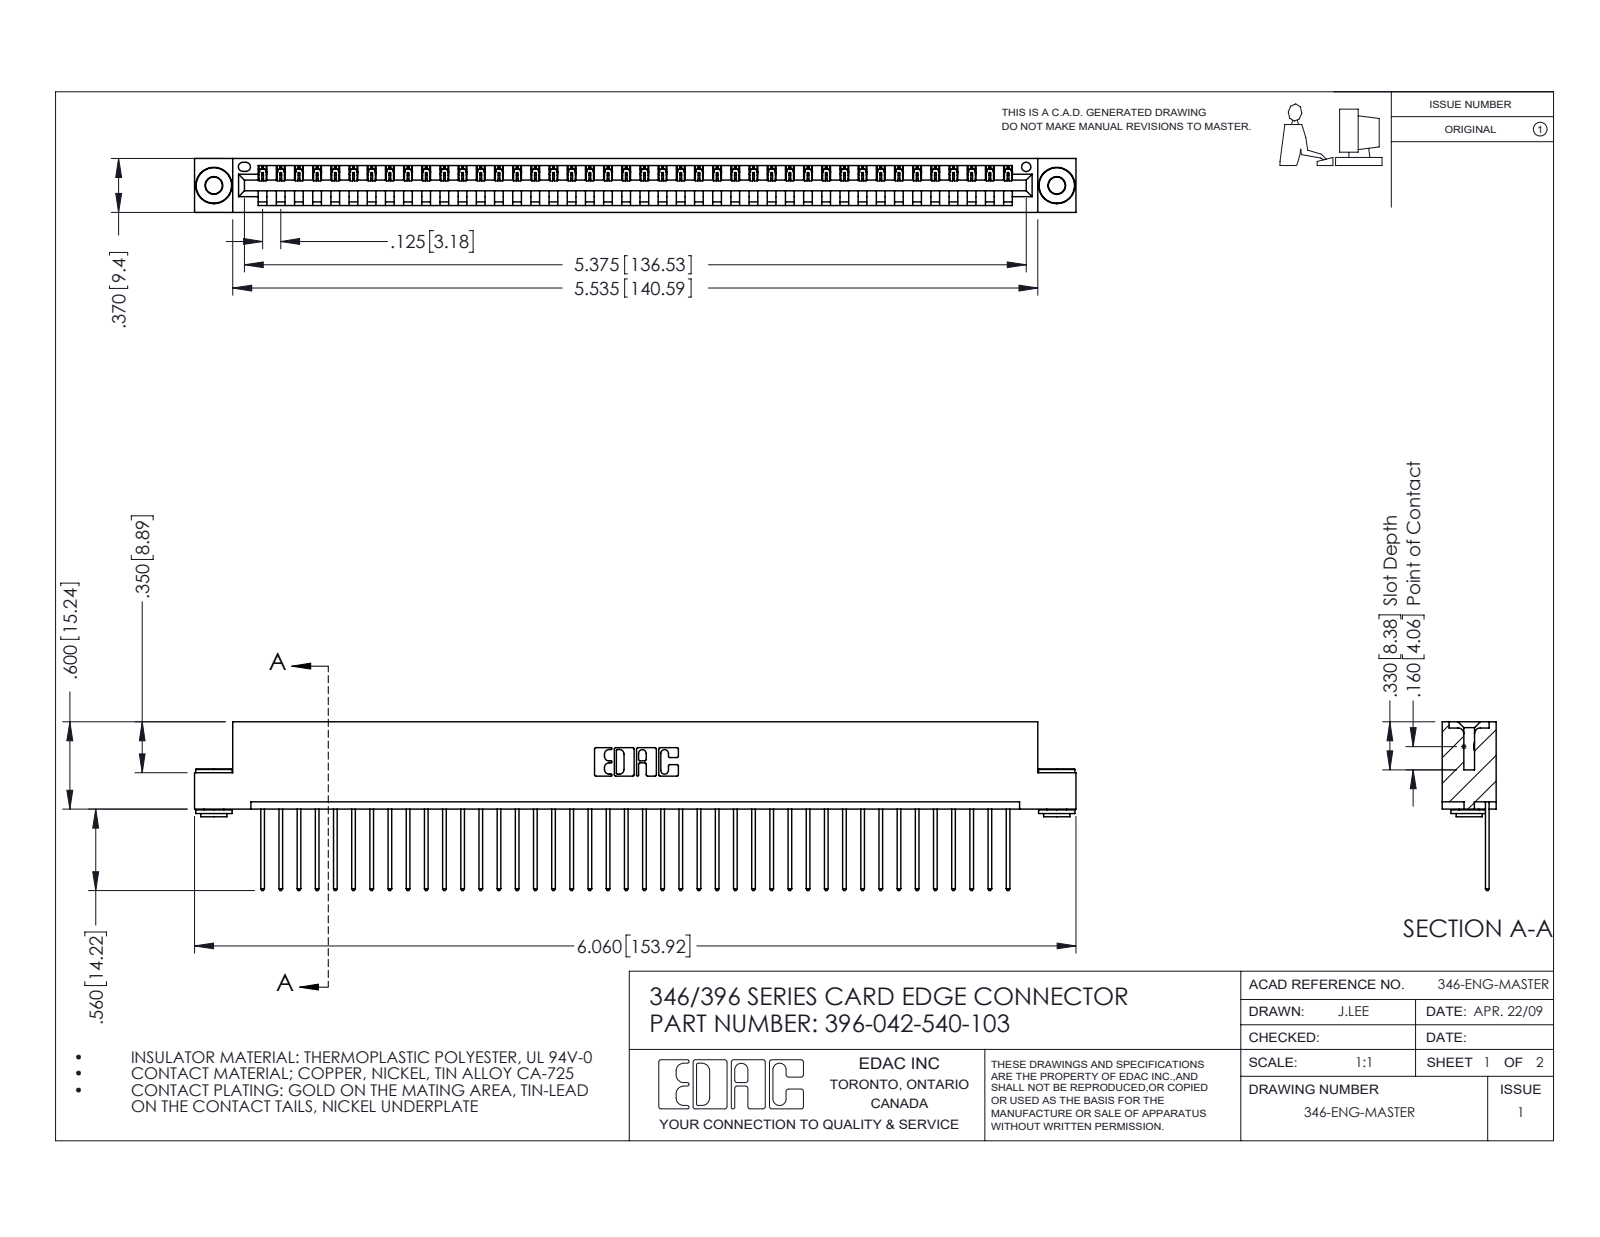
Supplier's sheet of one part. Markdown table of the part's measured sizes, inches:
| quantity | value |
| --- | --- |
| part name | 345-250-002_345-250-002-102; 345-292-001_345-293-140; 346 Part_Flush Mounting Lugs - 0.156 Dia-TH; 396-042-540-103 |
| STEP written by | SolidWorks 2016 (CONFIG_CONTROL_DESIGN) |
| units | inches |
| bodies | 45 solids, 2596 faces (1766 planar, 822 cylindrical, 8 other) |
| overall size | 6.06 × 1.16 × 0.37 |
| volume | 0.904 in³ |
| surface area | 29.68 in² |
| round holes (diameter × count) | 0.116 × 2, 0.156 × 2, 0.064 × 1 |
| round bosses / shafts (diameter × count) | 0.25 × 2, 0.18 × 2, 0.136 × 2 |
| partial cylindrical surfaces (radius × count) | 0.006 × 84, 0.01 × 84, 0.01 × 22, 0.007 × 6, 0.031 × 6, 0.026 × 3, 0.031 × 2, 0.04 × 2 |
| main face-to-face distances | 0.048, 0.322, 0.37, 0.25, 0.025, 0.072, 0.298, 0.148, 0.222, 0.1 |
| hole center spacings | 0.246, 5.586, 5.795 |
